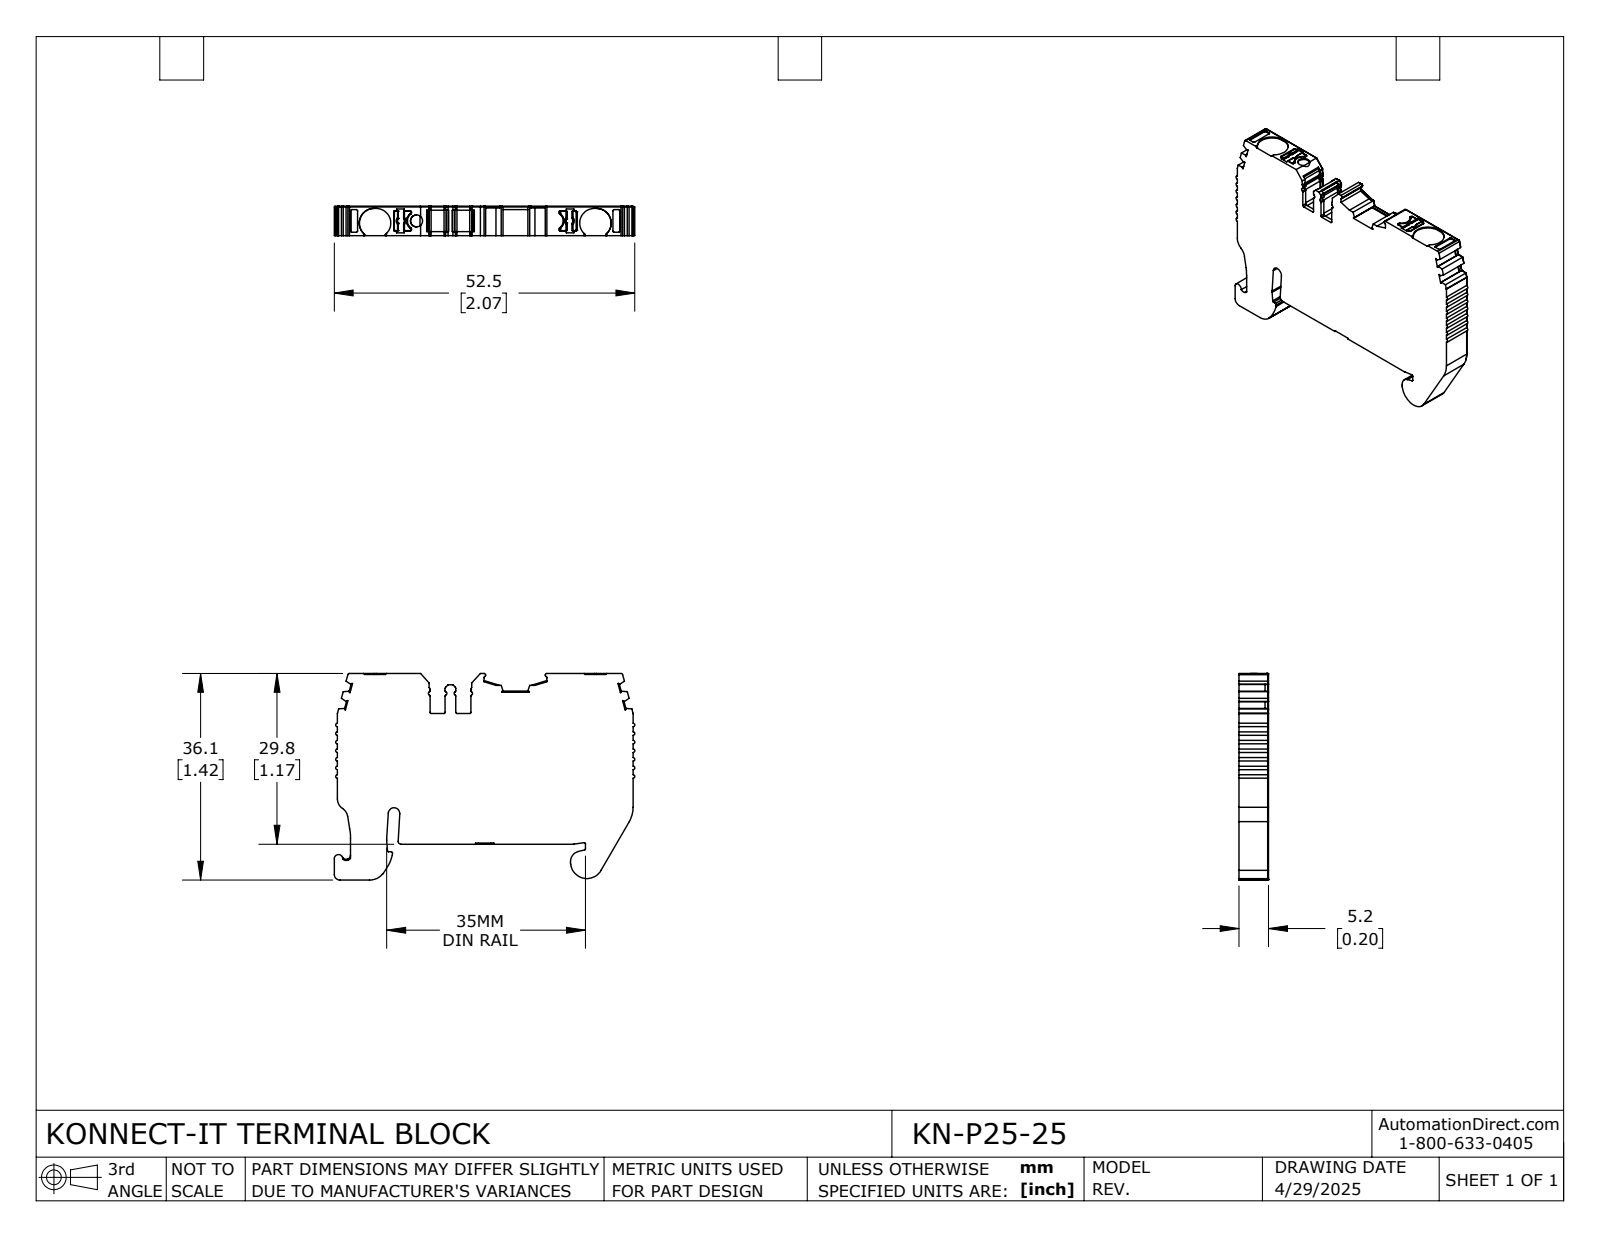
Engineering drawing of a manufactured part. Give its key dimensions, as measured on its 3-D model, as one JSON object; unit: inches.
{"part_name": "KN-P25-25", "step_written_by": "SolidWorks 2024 (CONFIG_CONTROL_DESIGN)", "units": "inches", "bodies": {"solids": 1, "faces": 584, "planar": 308, "cylindrical": 239, "other": 37}, "overall_size": [2.066, 1.42, 0.203], "volume_in3": 0.468, "surface_area_in2": 6.63, "round_holes": [[0.083, 1]], "partial_cylinders_radius": [[0.008, 54], [0.012, 39], [0.02, 18], [0.004, 17], [0.016, 9], [0.006, 8], [0.1, 4], [0.039, 3]], "face_to_face_distances": [0.203, 1.166, 1.174, 2.033, 0.177, 0.197, 0.246, 1.412, 0.079, 1.42]}
